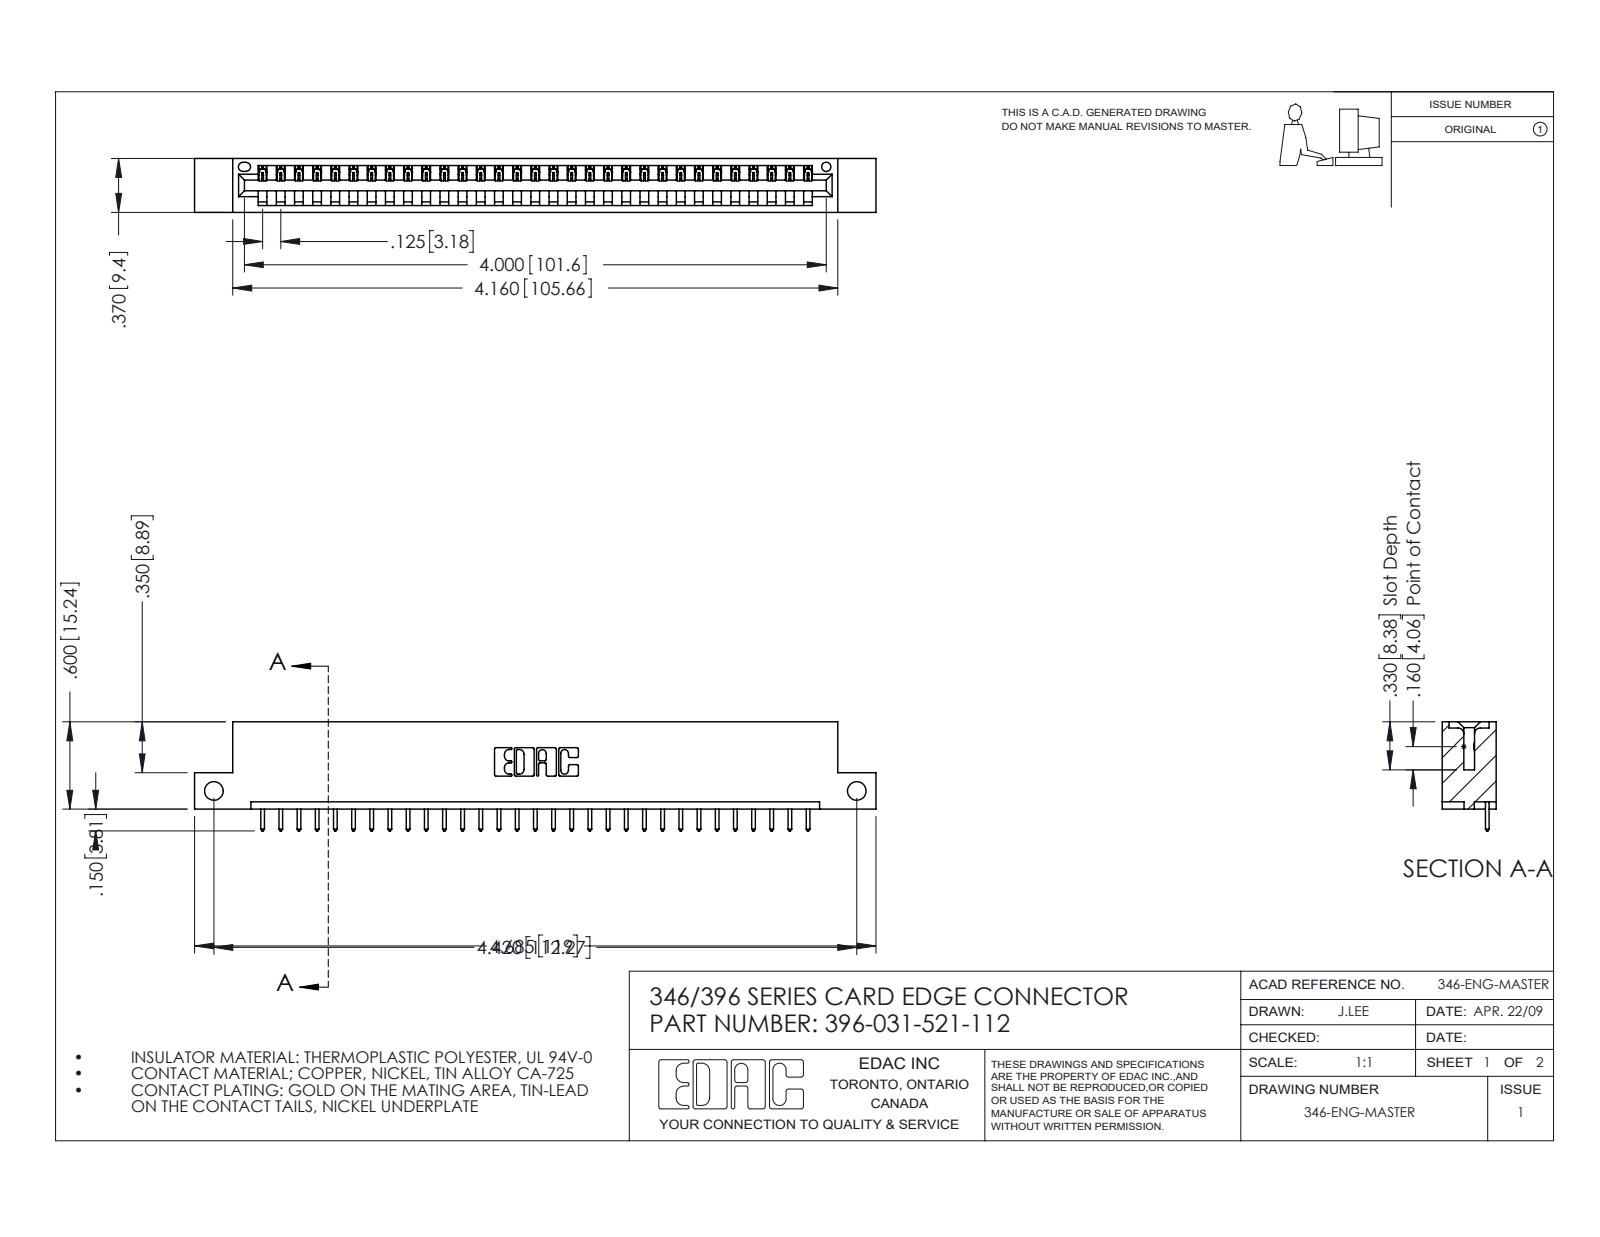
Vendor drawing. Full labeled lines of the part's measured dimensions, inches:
Part name (STEP PRODUCT): 396-031-521-112; 346 Part_Flush Mounting Lugs - Side Mount; 345-292-001_345-293-121
STEP written by: SolidWorks 2016 (CONFIG_CONTROL_DESIGN)
Units: inches
Bodies: 32 solids, 1920 faces (1316 planar, 604 cylindrical, 0 other)
Overall size (bounding box): 4.685 × 0.75 × 0.37
Volume: 0.68 in³ · Surface area: 20.63 in²
Round holes (diameter × count): ⌀0.128 ×2, ⌀0.064 ×1
Partial cylindrical surfaces — rounded edges, fillets, slot ends (radius × count): R0.006 ×62, R0.01 ×62, R0.01 ×22, R0.007 ×6, R0.031 ×6, R0.026 ×3, R0.031 ×2, R0.04 ×2
Main face-to-face distances: 0.048, 0.322, 0.37, 0.25, 0.072, 0.298, 0.025, 0.148, 0.222, 0.1
Hole centre spacings: 4.42
